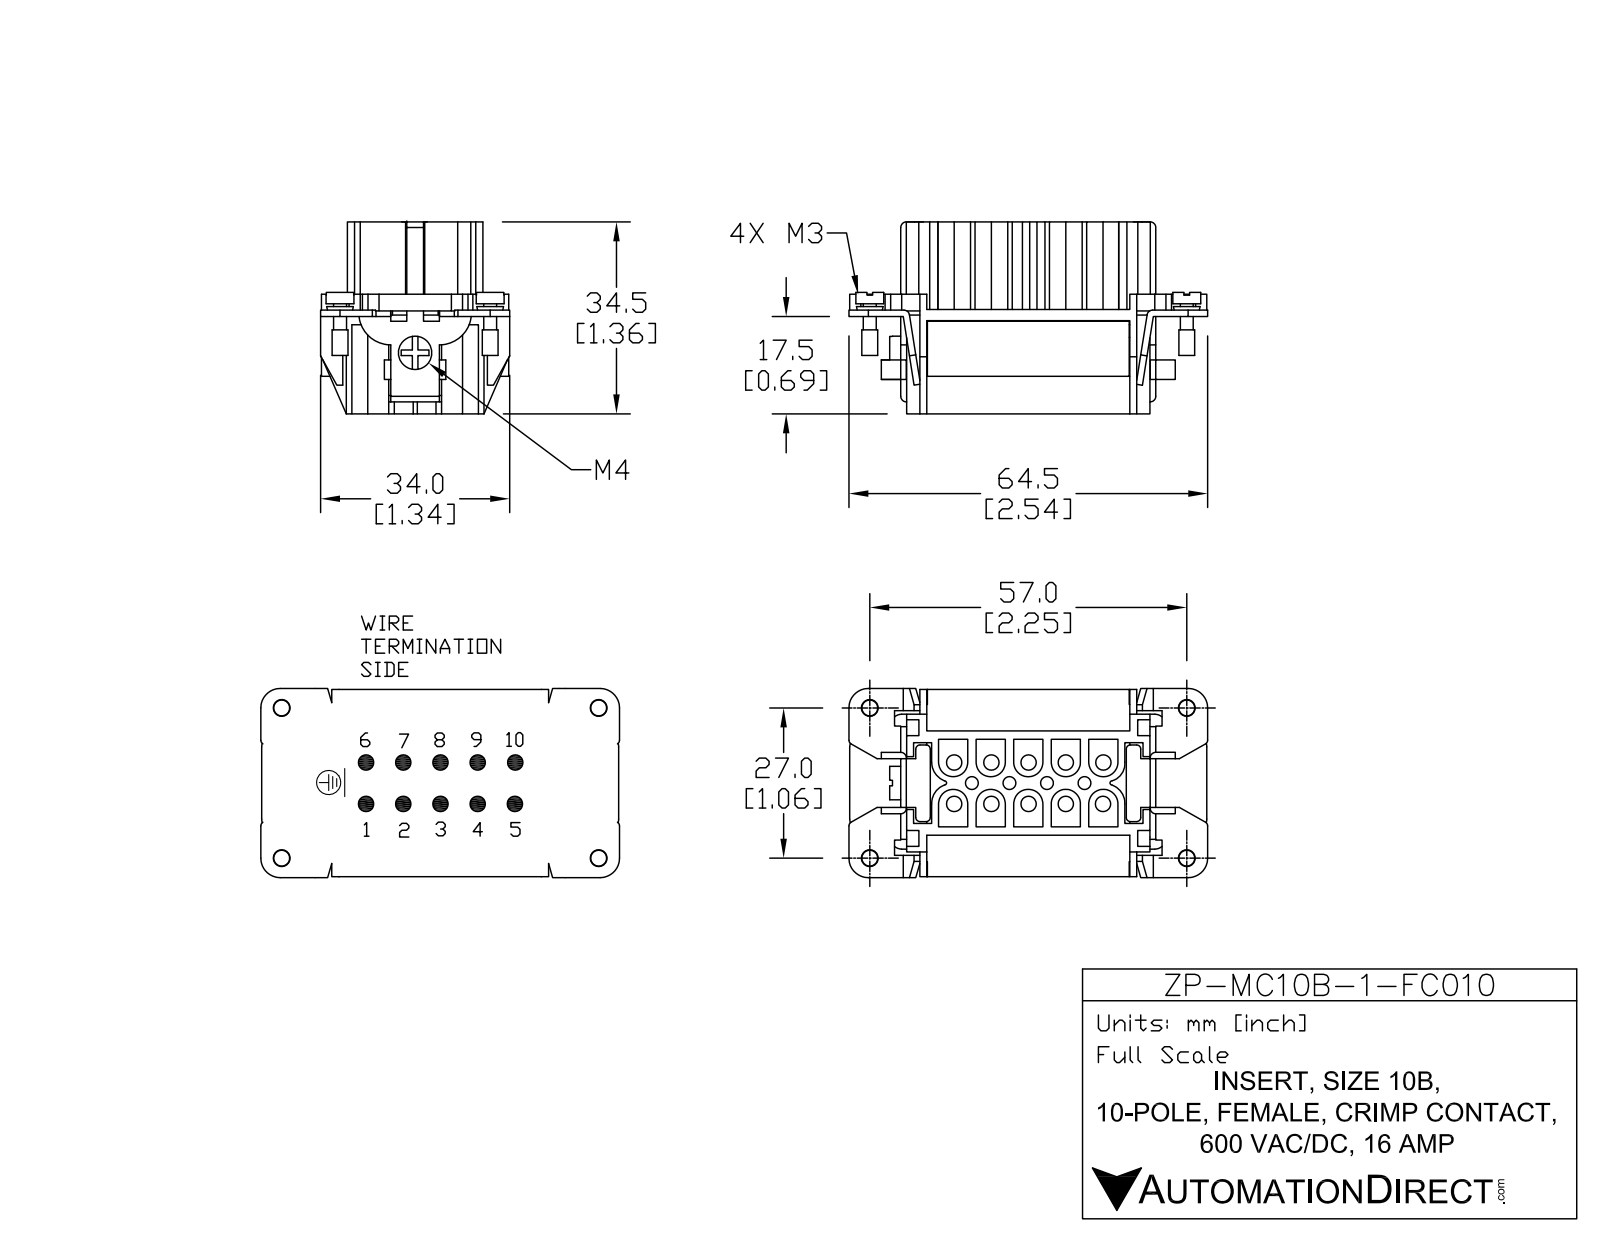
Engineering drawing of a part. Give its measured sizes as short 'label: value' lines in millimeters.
name: ZP-10B-10-FC-INSERT
written by: SolidWorks 2011 (AUTOMOTIVE_DESIGN)
unit: mm
bodies: 5 solids, 720 faces (555 planar, 121 cylindrical, 44 other)
size: 64.5 × 34.5 × 34
volume: 28 104 mm³; area: 21 079 mm²
holes: 10× ⌀2.75, 10× ⌀5.72, 4× ⌀1.75, 4× ⌀2.3, 4× ⌀3.01, 1× ⌀3
bosses: 4× ⌀5.02, 4× ⌀2.85, 4× ⌀2.32, 1× ⌀6
rounds: 14× R1, 12× R0.75, 10× R2.62, 10× R2.62, 8× R2, 4× R3.5, 4× R5.75, 2× R0.37
face distances: 12, 2, 1, 1.25, 2.75, 0.75, 1.15, 14.75, 3, 11.9
hole spacings: 6.69, 10.01, 6.75, 7.44, 13.38, 15.31, 22.81, 4.96
